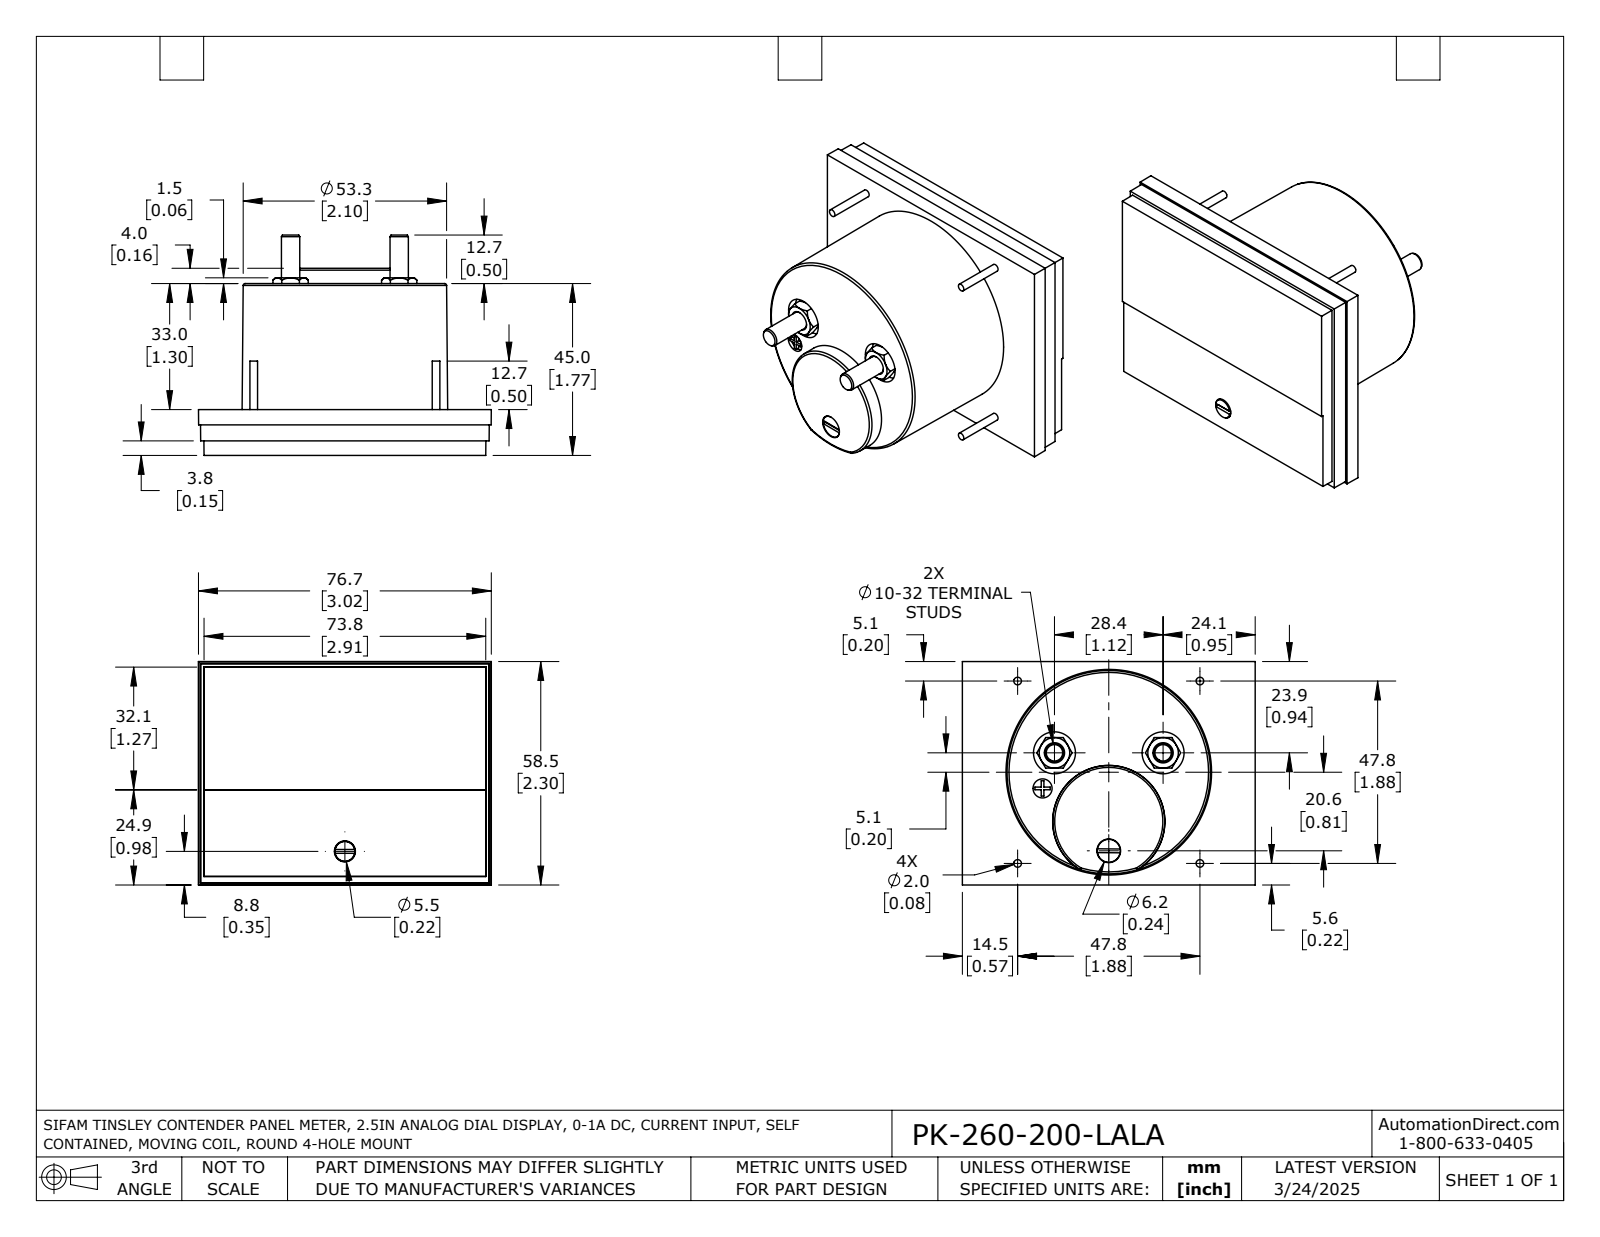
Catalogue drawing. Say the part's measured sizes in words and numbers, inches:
The part is named "PK-260-200-LALA". Its 3-D file was written by "SolidWorks 2021 (AUTOMOTIVE_DESIGN)". It is 1 solid with 192 faces: 95 planar, 37 cylindrical and 60 other. Overall it measures 3.02 by 2.303 by 2.272 inches. Its volume is 7.657 cubic inches and its surface area 36.55 square inches. Round holes: 3 of diameter 0.197, 2 of diameter 0.433, 1 of diameter 0.209, 1 of diameter 0.217, 1 of diameter 0.244. Round bosses or shafts: 4 of diameter 0.079, 2 of diameter 0.189, 1 of diameter 0.236, 1 of diameter 0.205. Partial cylindrical surfaces (rounded edges, fillets, slot ends): 1 of radius 0.033. The main face-to-face distances are 0.02, 0.472, 0.13, 0.322, 0.15, 0.453, 0.057, 0.077, 0.396, 0.073. The hole center spacings are 1.155, 1.16, 0.387, 0.938, 0.942, 1.12, 1.295.
